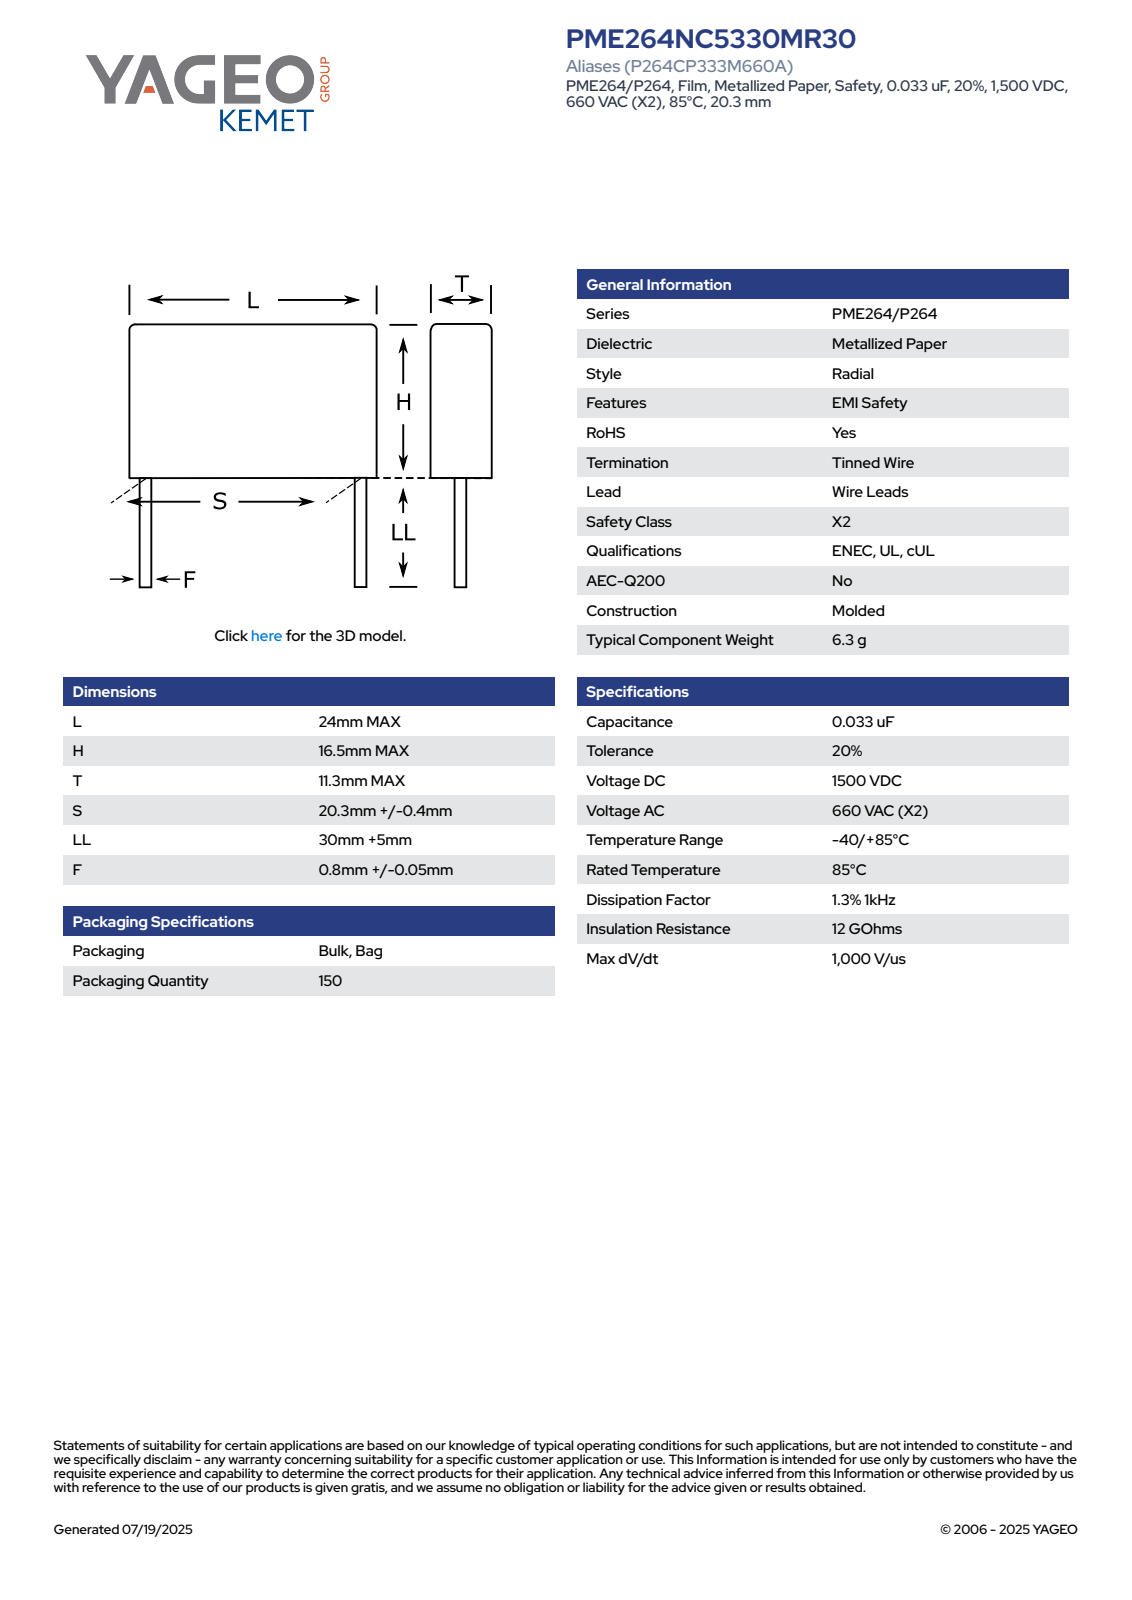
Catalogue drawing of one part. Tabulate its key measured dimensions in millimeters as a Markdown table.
| quantity | value |
| --- | --- |
| part name | CFR_MOLDED_24X16.5X11.3_L24H16.5T11.3S20.3LL35F0.8 |
| STEP written by | SolidWorks 2014 (AUTOMOTIVE_DESIGN) |
| units | millimeters |
| bodies | 4 solids, 73 faces (65 planar, 8 cylindrical, 0 other) |
| overall size | 51.5 × 24 × 11.3 |
| volume | 4 506 mm³ |
| surface area | 1 896 mm² |
| round bosses / shafts (diameter × count) | 0.8 × 2 |
| partial cylindrical surfaces (radius × count) | 0.5 × 4 |
| main face-to-face distances | 11.3, 16.5, 24, 11.31, 35, 51.5, 44.07, 9.07, 7.43, 41.92 |
